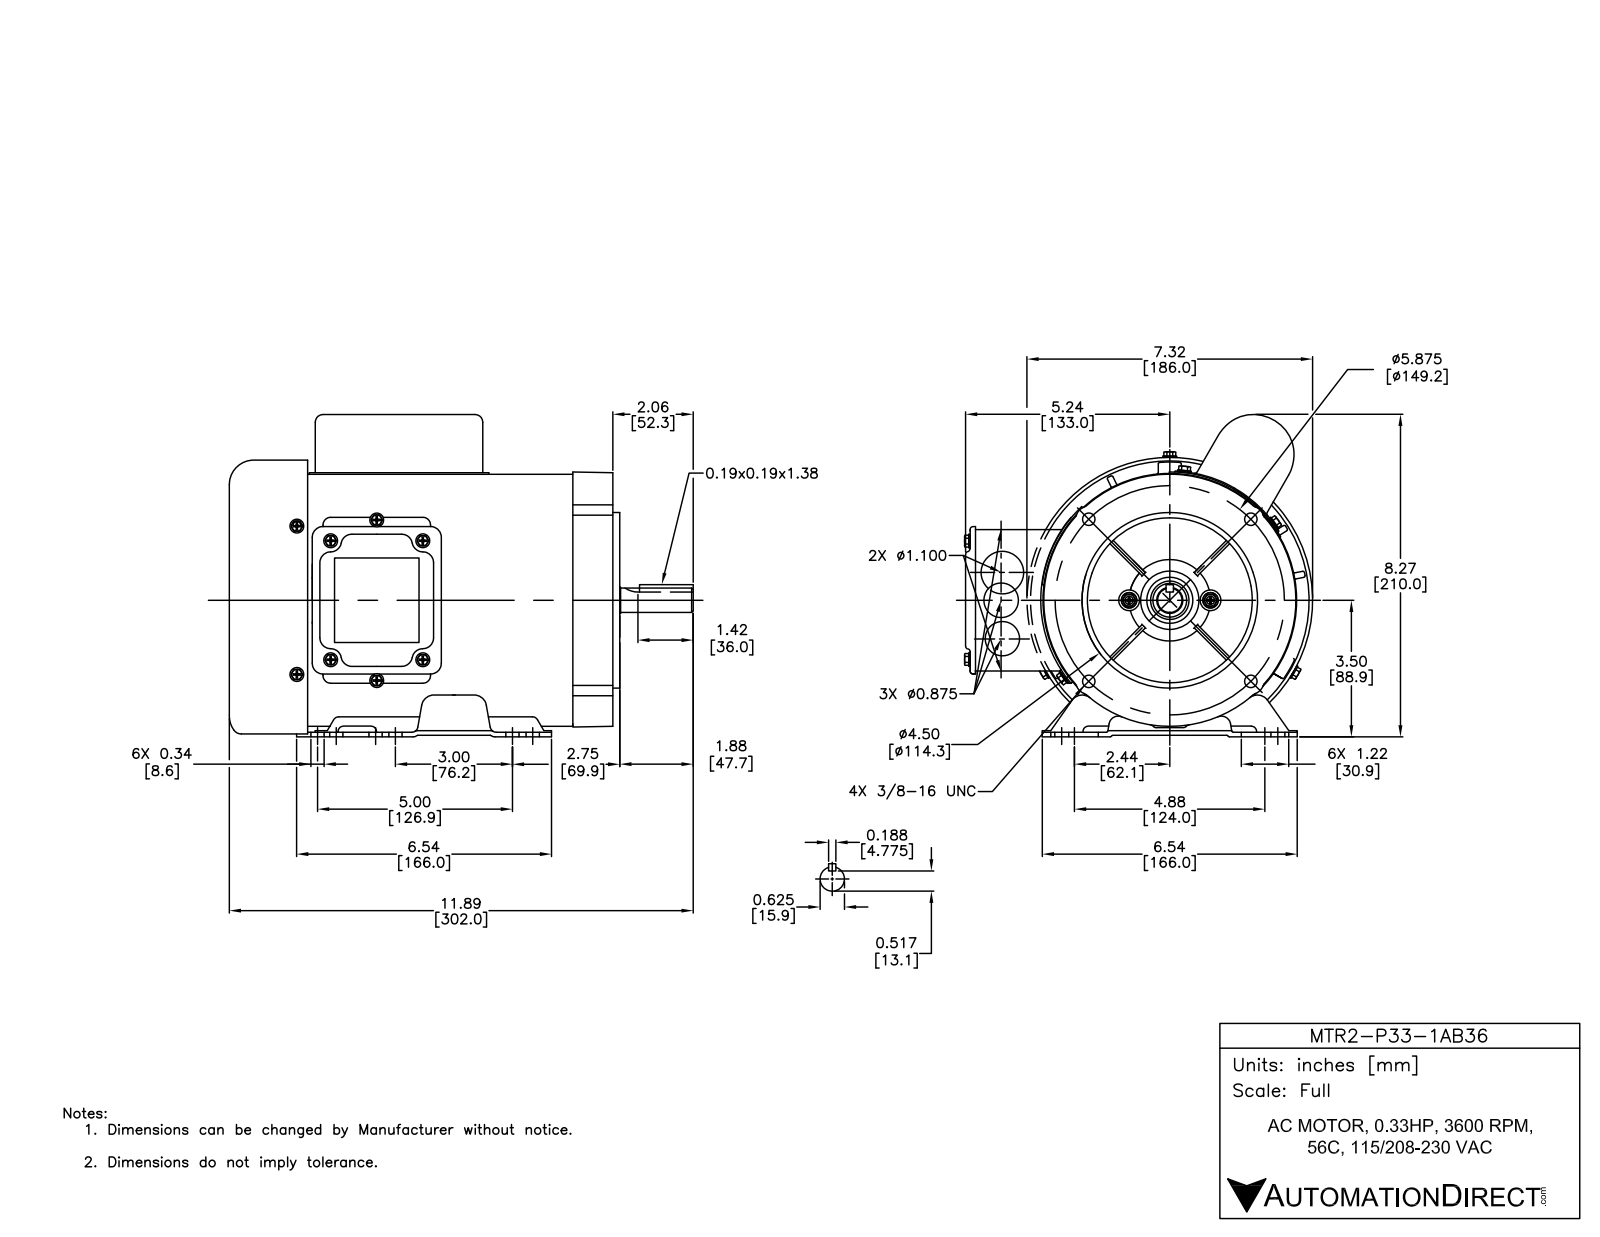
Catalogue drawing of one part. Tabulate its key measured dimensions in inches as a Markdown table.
| quantity | value |
| --- | --- |
| part name | Base; Elec Cover bolt Hex Washer Screw_AI_IN-HWMS 0.164-32x0.3125x0.3125-N; Cap cover bolt; Cap cover gasket (+8 more) |
| STEP written by | SolidWorks 2015 (AUTOMOTIVE_DESIGN) |
| units | inches |
| bodies | 54 solids, 2460 faces (924 planar, 1007 cylindrical, 529 other) |
| overall size | 11.89 × 10.026 × 9.765 |
| volume | 53.5 in³ |
| surface area | 1 095 in² |
| round holes (diameter × count) | 0.219 × 13, 0.197 × 12, 0.276 × 8, 0.217 × 6, 0.248 × 6, 0.344 × 6, 0.136 × 5, 0.154 × 4, 0.313 × 4, 0.709 × 3, 0.13 × 2, 0.134 × 2 |
| round bosses / shafts (diameter × count) | 0.348 × 13, 0.164 × 13, 0.248 × 4, 0.551 × 2, 0.414 × 2, 0.19 × 2, 7.185 × 1, 6.496 × 1 |
| partial cylindrical surfaces (radius × count) | 0.118 × 101, 0.039 × 66, 0.228 × 24, 0.075 × 23, 0.197 × 22, 0.276 × 17, 0.1 × 16, 0.12 × 14 |
| main face-to-face distances | 0.039, 0.236, 0.118, 1.403, 0.063, 8.386, 1.639, 0.075, 1.364, 1.6 |
| hole center spacings | 4.221, 3.031, 0.094, 2.937, 3.748, 4.154, 5.969, 2.32 |
